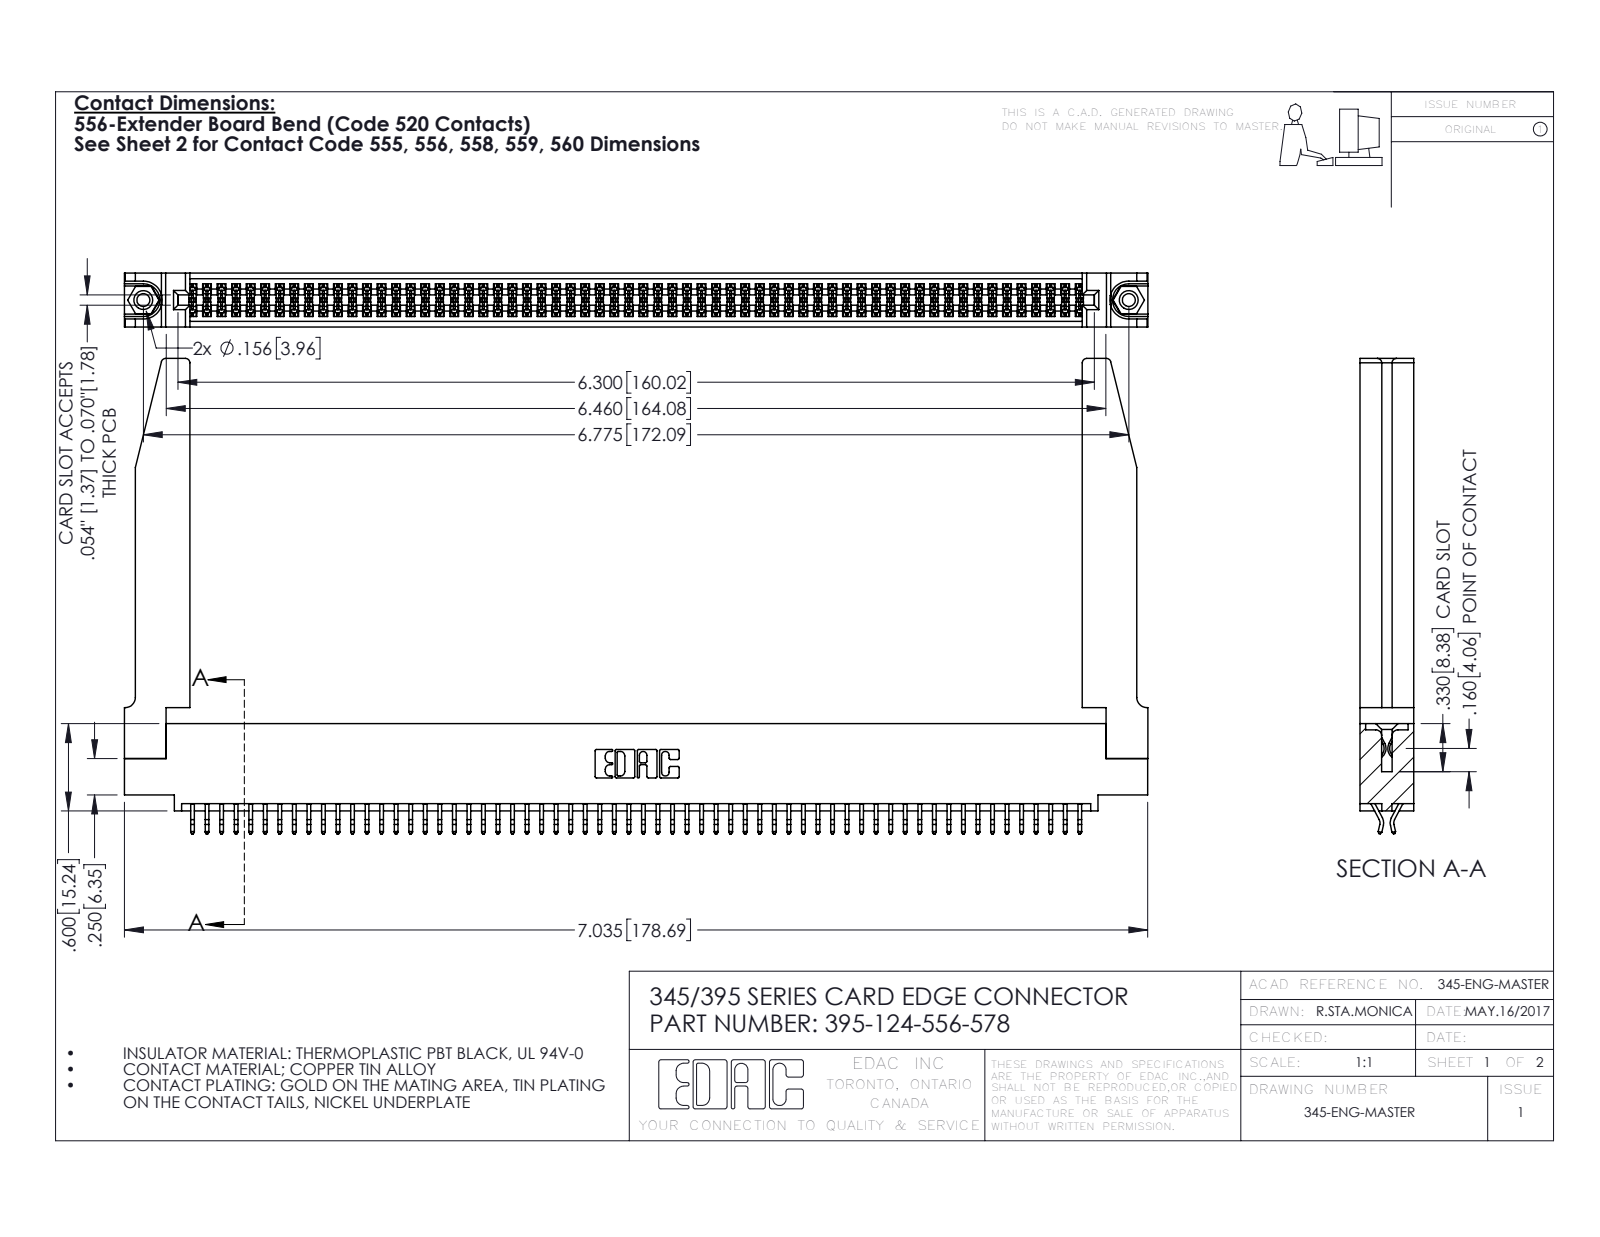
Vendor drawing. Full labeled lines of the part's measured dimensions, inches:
Part name (STEP PRODUCT): 395-124-556-578; 345 Part_0.110 Offset - 0.156 Dia-TH; 345-220-078_345-220-078; 345-250-001_345-250-001-102 (+1 more)
STEP written by: SolidWorks 2016 (CONFIG_CONTROL_DESIGN)
Units: inches
Bodies: 129 solids, 7308 faces (4814 planar, 2442 cylindrical, 52 other)
Overall size (bounding box): 7.036 × 3.267 × 0.37
Volume: 1.54 in³ · Surface area: 51.2 in²
Round holes (diameter × count): ⌀0.089 ×2, ⌀0.125 ×2, ⌀0.156 ×2, ⌀0.064 ×1
Round bosses / shafts (diameter × count): ⌀0.155 ×2
Partial cylindrical surfaces — rounded edges, fillets, slot ends (radius × count): R0.006 ×186, R0.01 ×22, R0.03 ×8, R0.007 ×6, R0.031 ×6, R0.026 ×3, R0.01 ×2, R0.014 ×2
Main face-to-face distances: 0.072, 0.298, 0.37, 0.025, 0.098, 0.272, 0.2, 0.225, 0.175, 0.148
Hole centre spacings: 0.27, 6.539, 6.775
